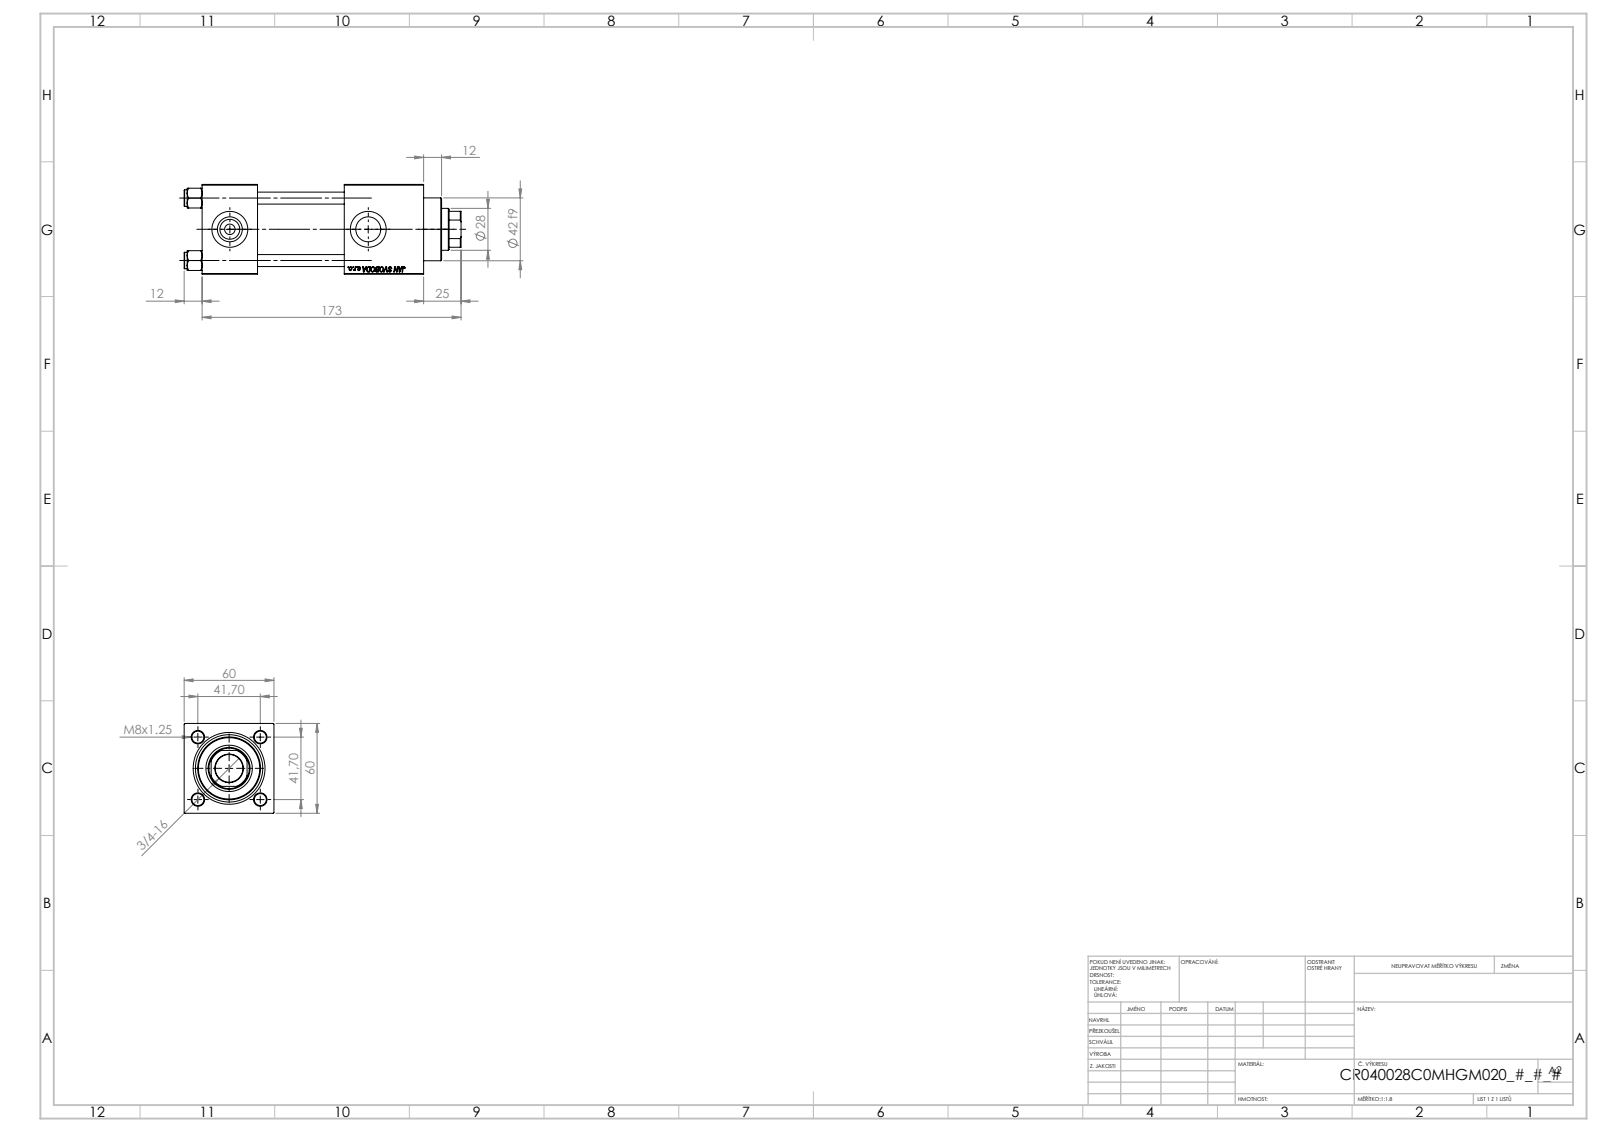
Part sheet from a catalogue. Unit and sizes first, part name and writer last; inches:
Units: inches
Overall size (bounding box): 7.283 × 2.362 × 2.362
Round holes (diameter × count): ⌀0.315 ×4, ⌀0.276 ×2, ⌀0.656 ×2, ⌀0.945 ×2, ⌀0.728 ×1, ⌀1.102 ×1, ⌀1.22 ×1, ⌀1.575 ×1, ⌀1.772 ×1
Round bosses / shafts (diameter × count): ⌀0.433 ×4, ⌀1.811 ×1, ⌀1.654 ×1
Partial cylindrical surfaces — rounded edges, fillets, slot ends (radius × count): R0.531 ×1
Main face-to-face distances: 2.362, 1.457, 2.283, 3.74, 2.087, 4.697, 3.24, 0.957, 5.827, 4.37
Hole centre spacings: 1.161, 1.642, 2.322, 3.642
Volume: 25.89 in³ · Surface area: 172.7 in²
Bodies: 11 solids, 1148 faces (526 planar, 86 cylindrical, 536 other)
Part name (STEP PRODUCT): V215CR_VCP_C; V215CR_C_TYCINKA; NUT_M5_C; V215_VC_A (+1 more)
STEP written by: SolidWorks 2019 (CONFIG_CONTROL_DESIGN)
